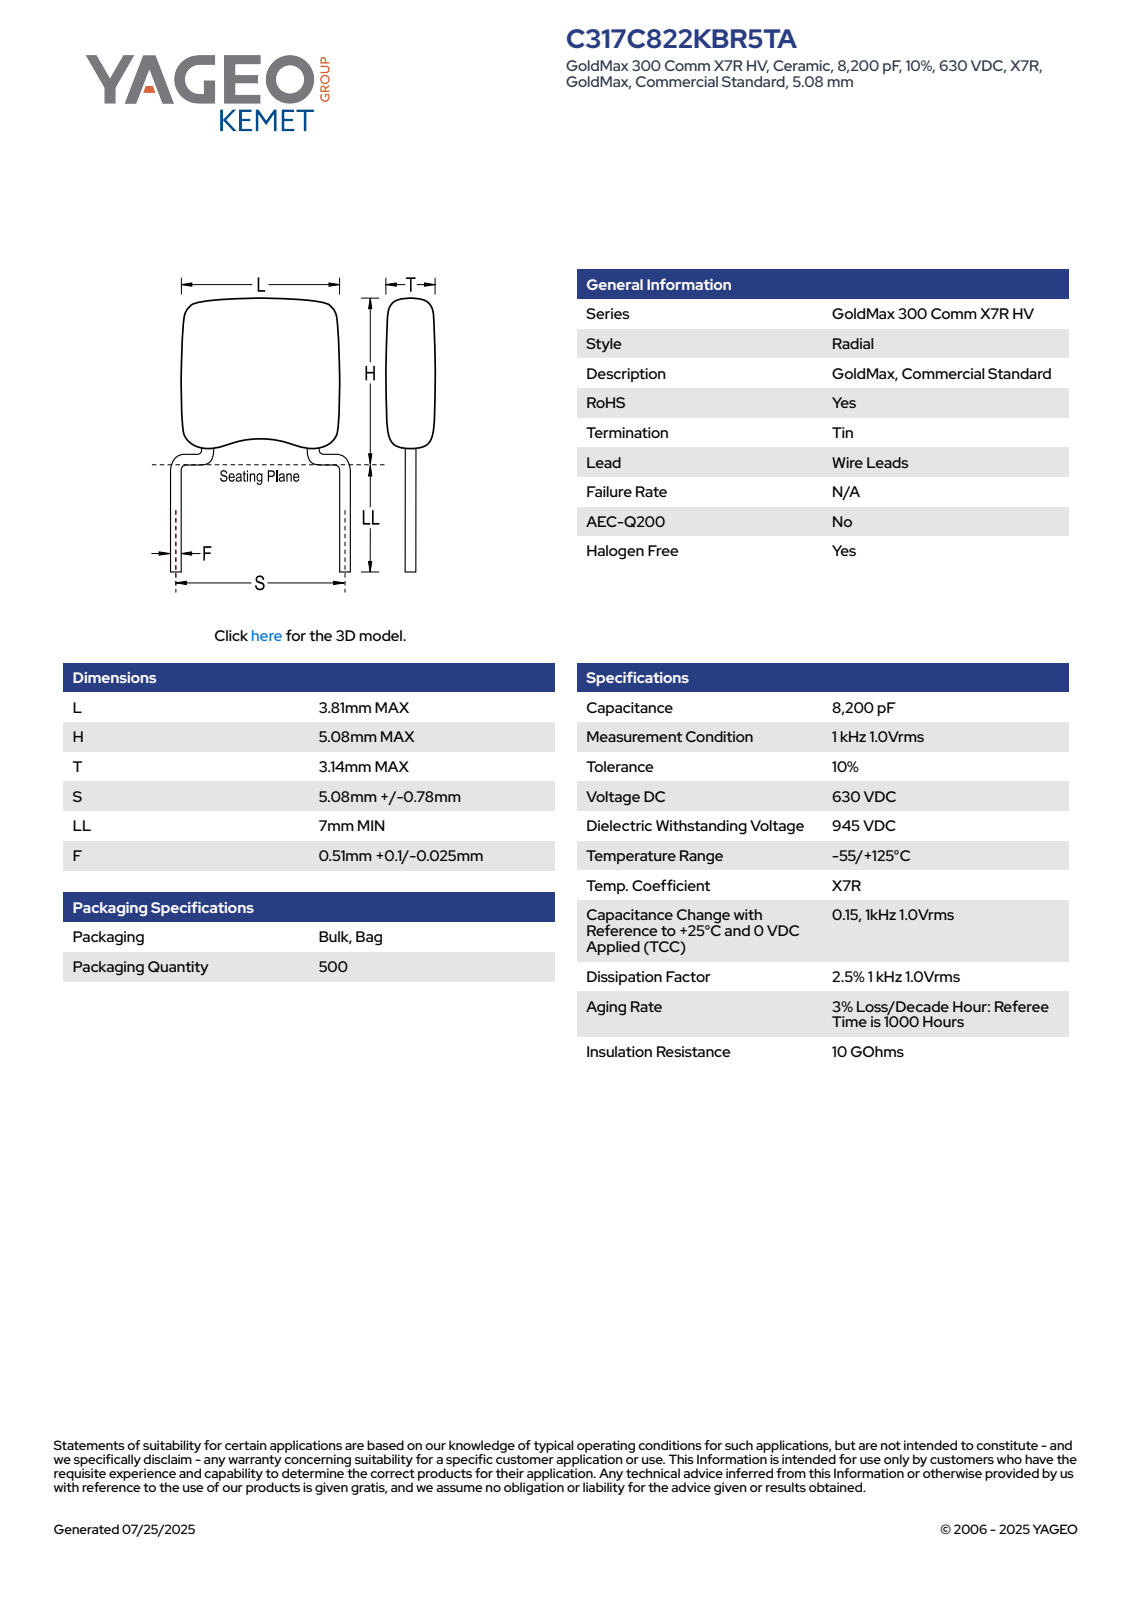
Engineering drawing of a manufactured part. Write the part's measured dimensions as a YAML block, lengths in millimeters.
part_name: "CCR_SB_3.81X5.08_L3.81H5.08T3.14S5.08LL7F0.51"
step_written_by: "SolidWorks 2014 (AUTOMOTIVE_DESIGN)"
units: millimeters
bodies: {solids: 4, faces: 97, planar: 65, cylindrical: 14, other: 18}
overall_size: [12.08, 5.59, 3.15]
volume: 40
surface_area: 88
round_bosses_or_shafts:
  - {diameter: 0.51, count: 2}
partial_cylinders:
  - {radius: 1, count: 10}
face_to_face_distances: [3.14, 3.81, 3.61, 0.32, 1.98, 1.63, 1.66, 1.95, 0.41, 1.32]
